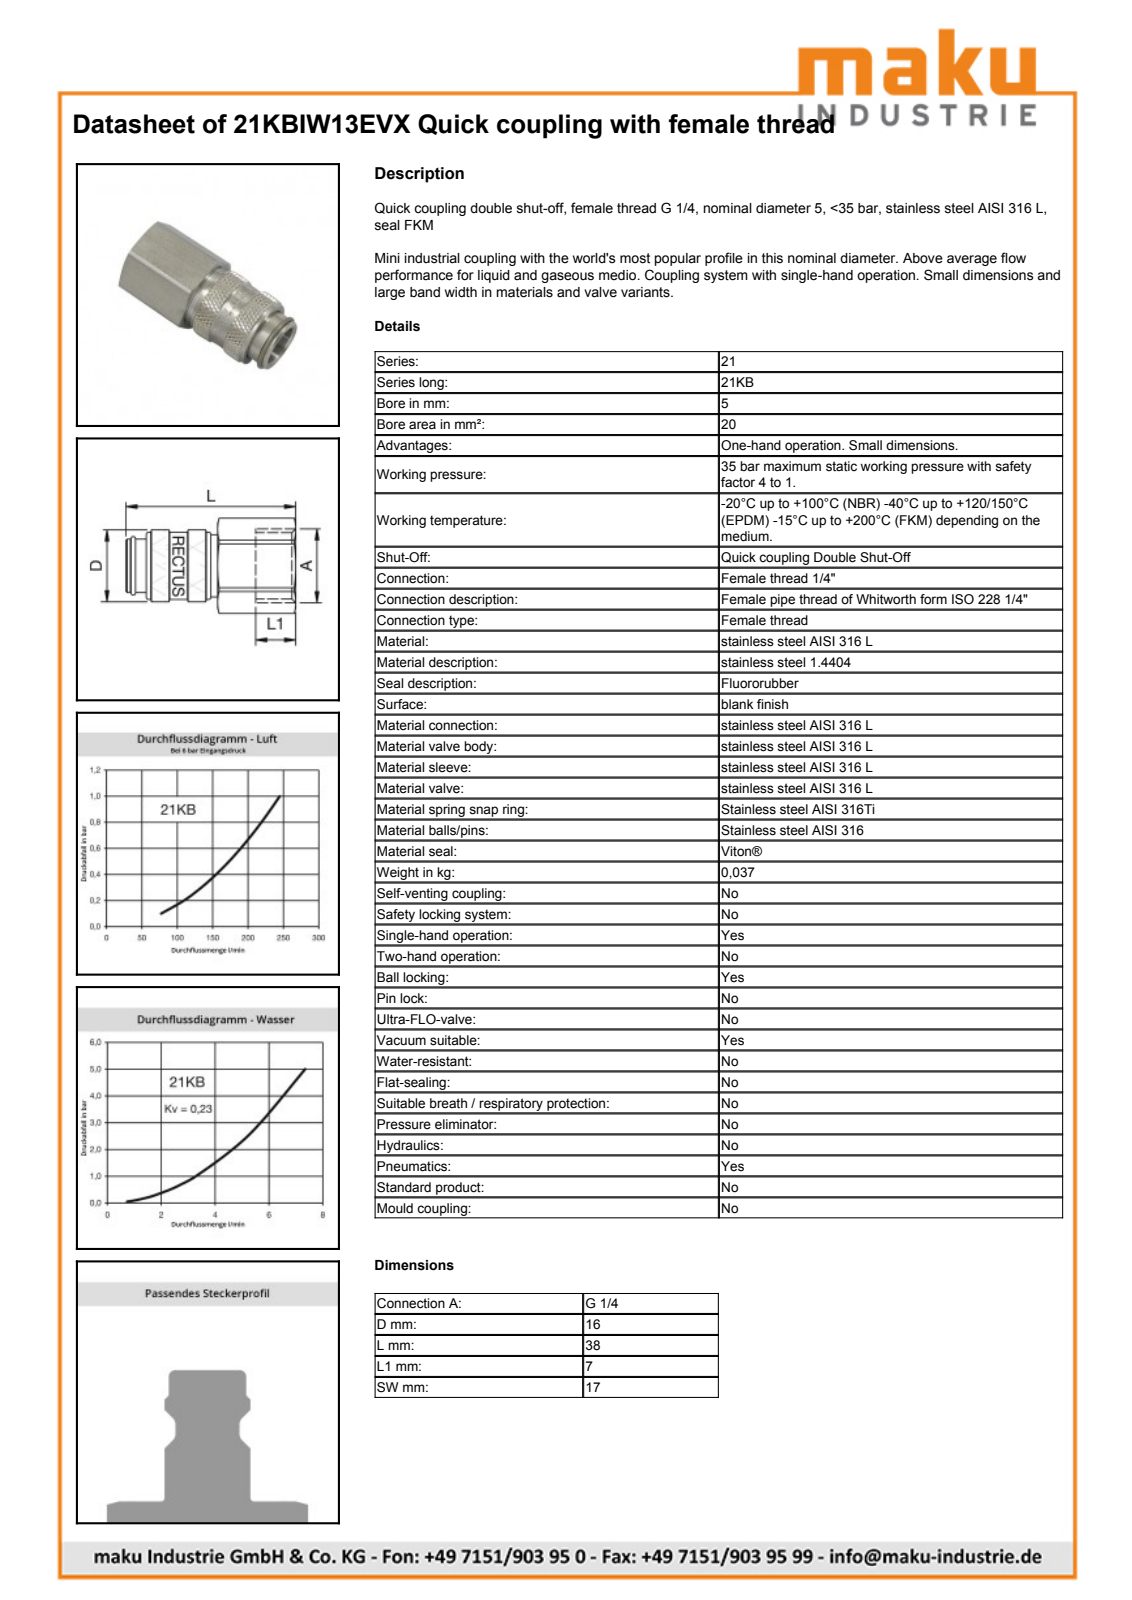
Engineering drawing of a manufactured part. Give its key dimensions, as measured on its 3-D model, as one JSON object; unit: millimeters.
{"part_name": "D110770", "step_written_by": "Autodesk Inventor 2013 (AUTOMOTIVE_DESIGN)", "units": "millimeters", "bodies": {"solids": 2, "faces": 402, "planar": 165, "cylindrical": 65, "other": 172}, "overall_size": [38.15, 19.04, 18.13], "volume_mm3": 6673, "surface_area_mm2": 4269, "round_holes": [[7.5, 1], [11.45, 1], [12.15, 1], [14, 1]], "round_bosses_or_shafts": [[16.15, 1], [15.1, 1], [12, 1], [11.4, 1], [11.15, 1], [10.86, 1]], "partial_cylinders_radius": [[7.45, 1], [9.57, 1]], "face_to_face_distances": [17, 38.15, 20.6, 17.55, 9, 29.15, 8.55, 29.14, 8.54, 9.01]}
